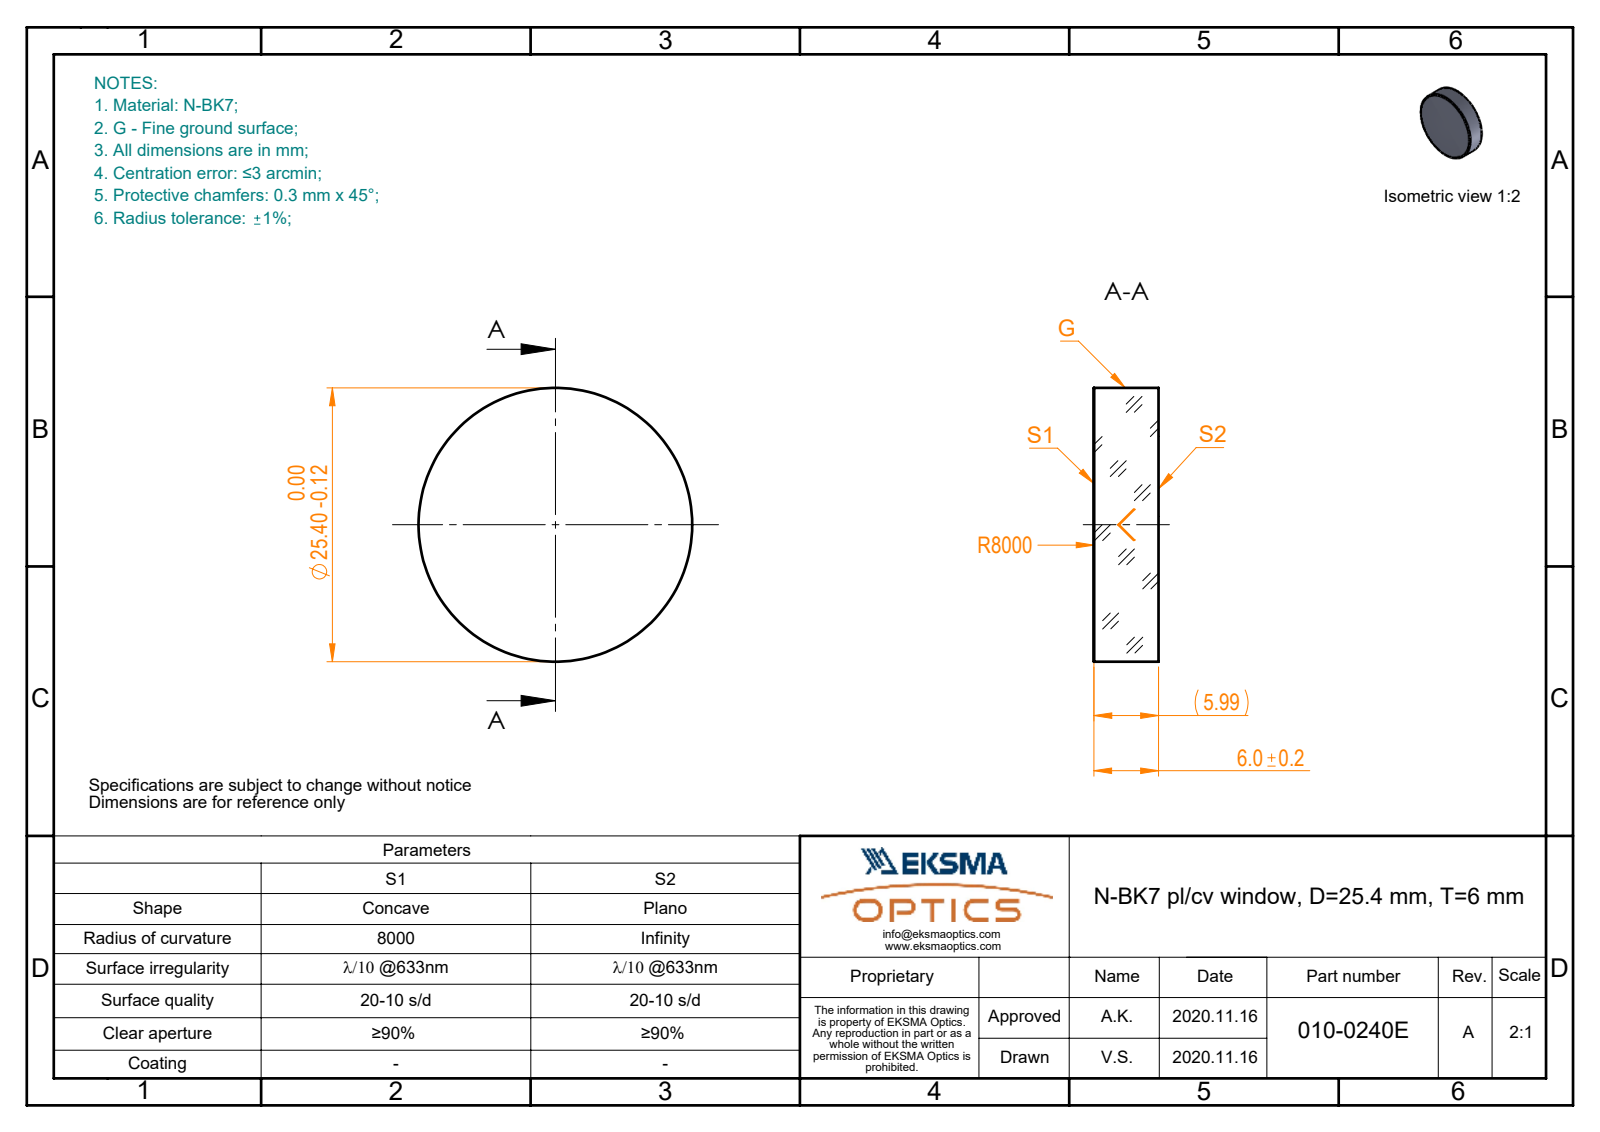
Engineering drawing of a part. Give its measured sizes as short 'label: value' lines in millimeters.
name: 010-0240E_N-BK7_PCV_window
written by: SolidWorks 2019 (CONFIG_CONTROL_DESIGN)
unit: mm
bodies: 1 solid, 5 faces (1 planar, 2 cylindrical, 2 other)
size: 25.4 × 25.4 × 6
volume: 3 038 mm³; area: 1 492 mm²
bosses: 1× ⌀25.4
